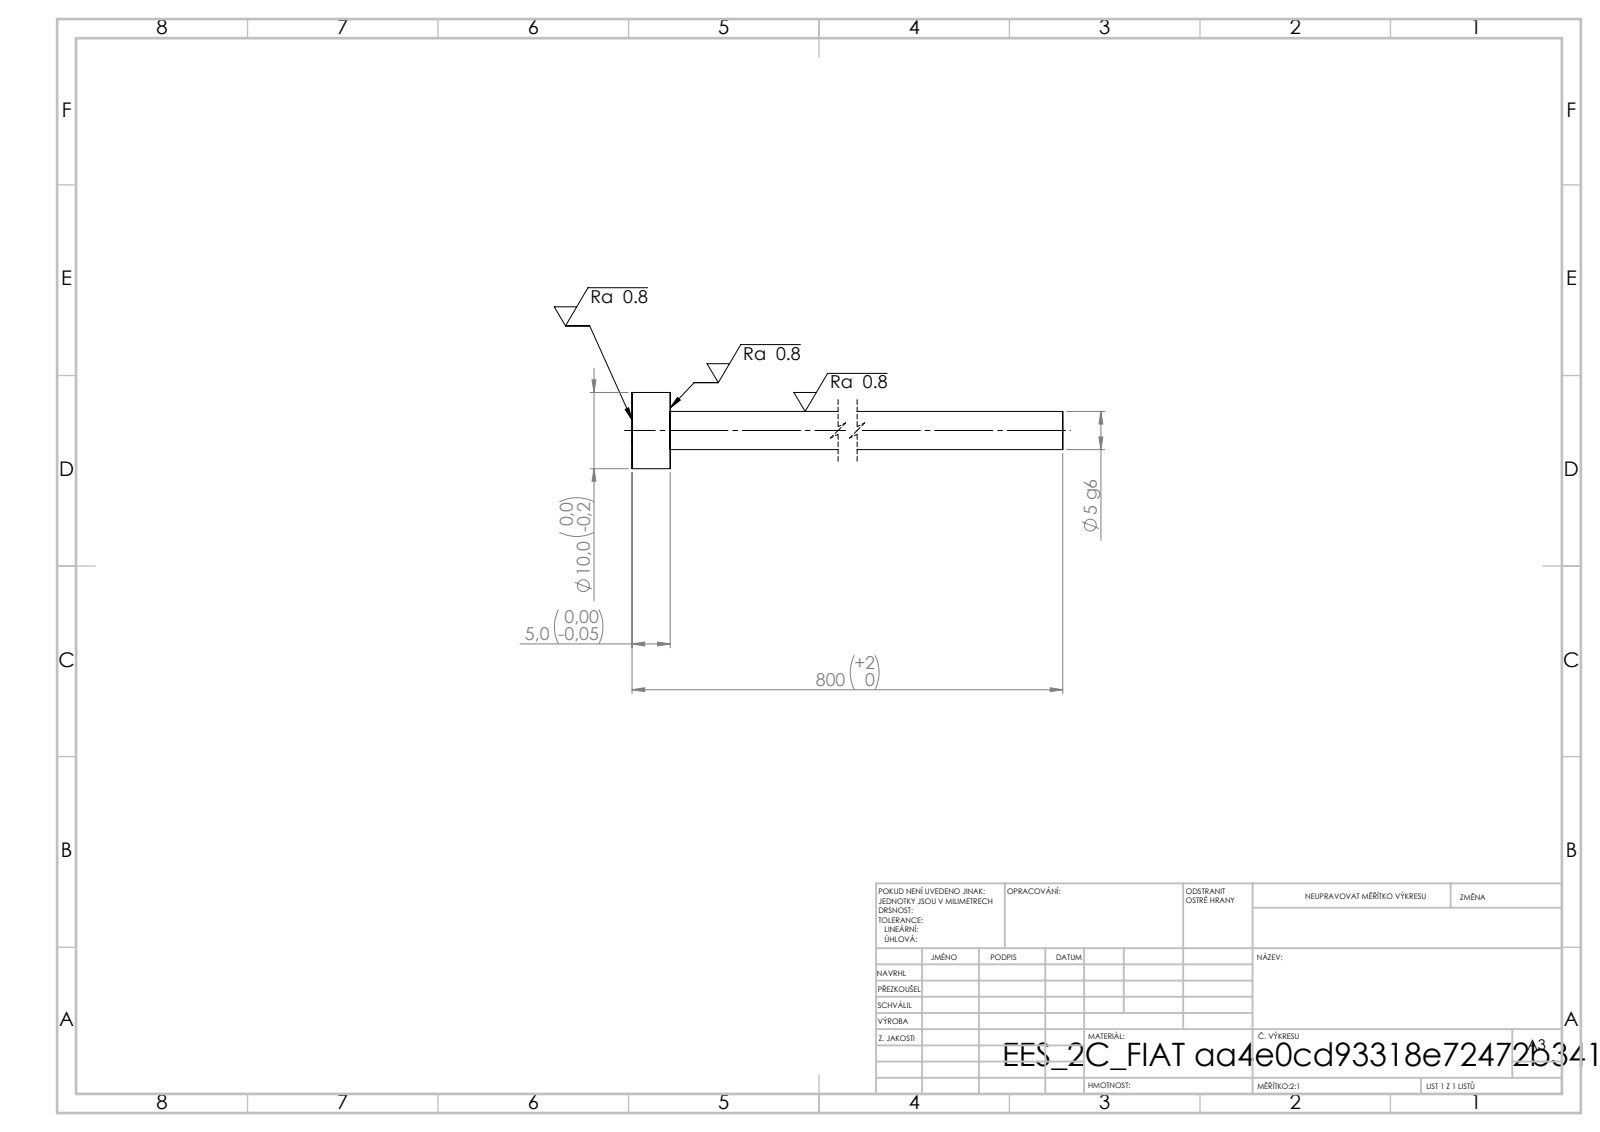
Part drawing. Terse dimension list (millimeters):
written by: SolidWorks 2019 (CONFIG_CONTROL_DESIGN)
unit: mm
bodies: 1 solid, 7 faces (3 planar, 4 cylindrical, 0 other)
size: 800 × 10 × 10
volume: 16 002 mm³; area: 12 802 mm²
bosses: 1× ⌀10, 1× ⌀5
face distances: 5, 800, 795
